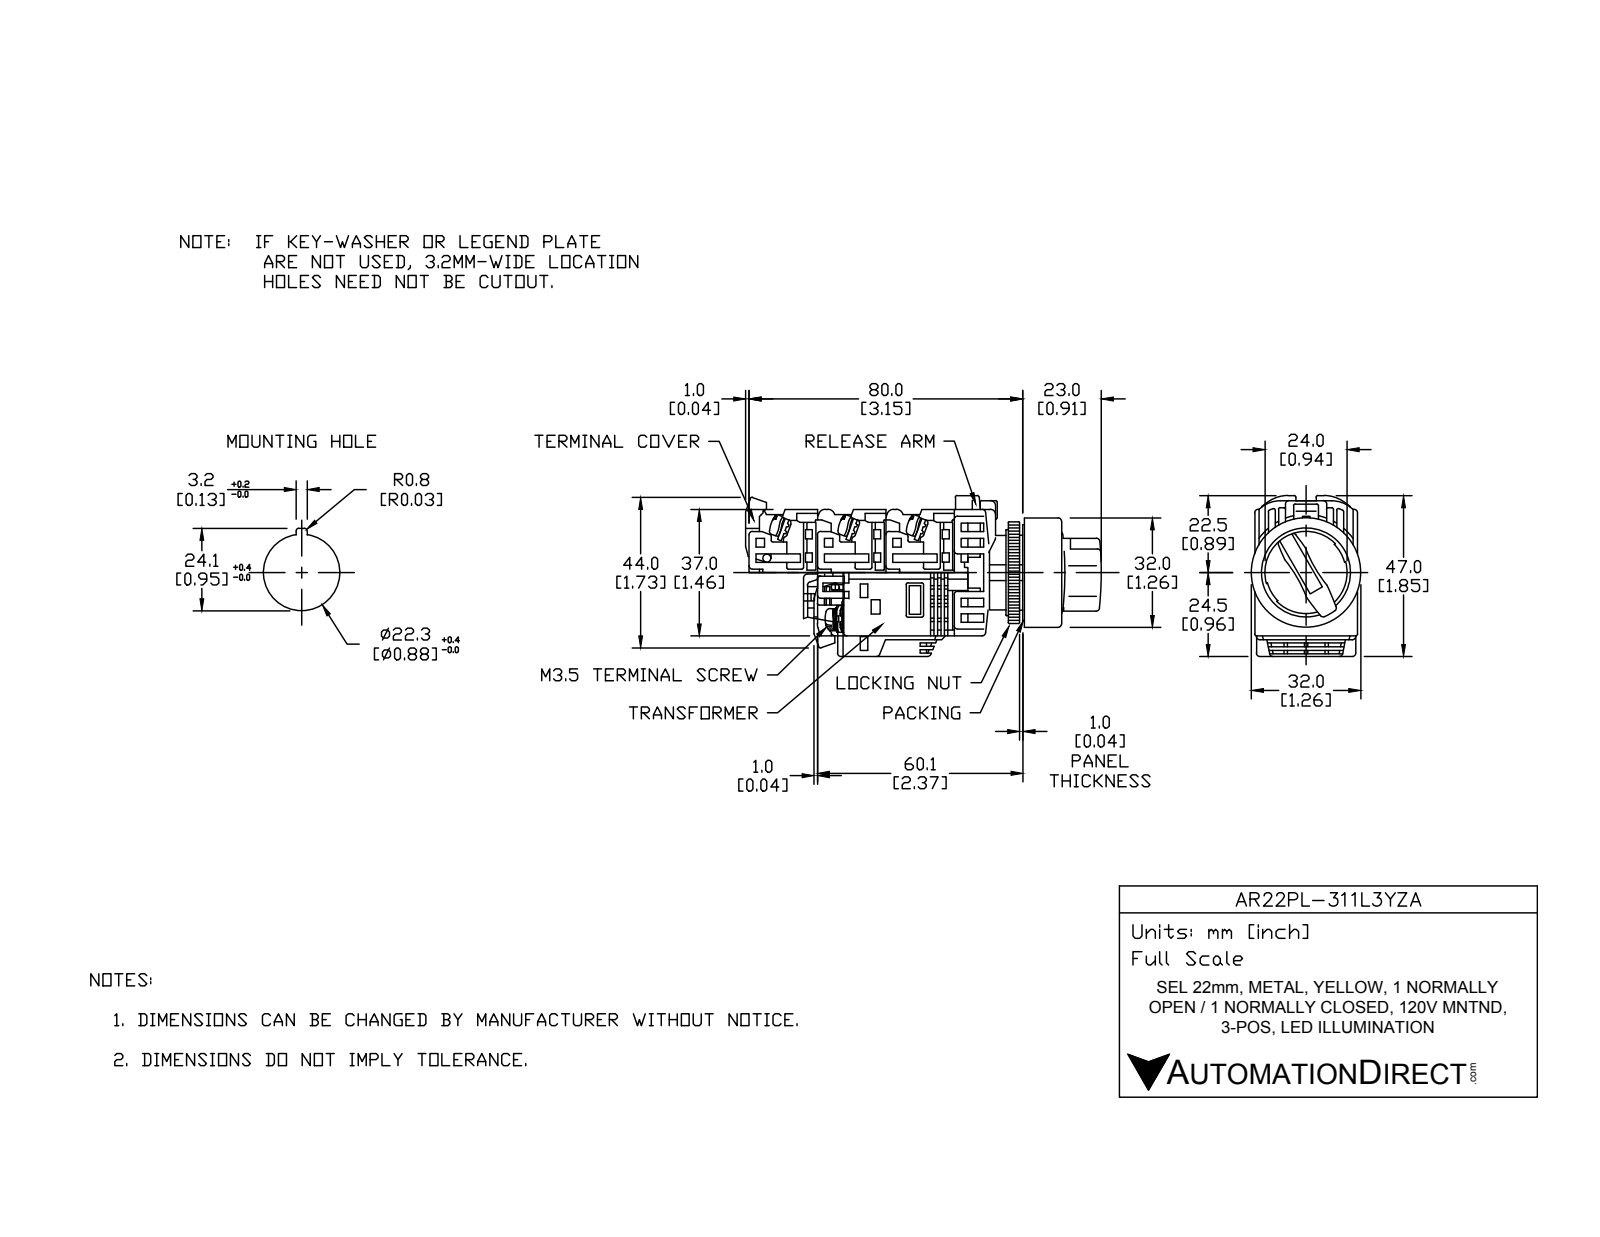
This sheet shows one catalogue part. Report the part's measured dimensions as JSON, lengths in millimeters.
{"part_name": "AR22PL-311L3YZA", "step_written_by": "SolidWorks 2017 (AUTOMOTIVE_DESIGN)", "units": "millimeters", "bodies": {"solids": 24, "faces": 602, "planar": 413, "cylindrical": 155, "other": 34}, "overall_size": [84.5, 43.81, 32], "volume_mm3": 58015, "surface_area_mm2": 31382, "round_holes": [[21.8, 1], [22, 1], [25, 1], [31, 1]], "round_bosses_or_shafts": [[5, 6], [32, 1], [30.5, 1], [29.8, 1], [24, 1], [21.75, 1], [17, 1]], "partial_cylinders_radius": [[0.5, 55], [1.75, 12], [1, 6], [5, 4], [4, 2], [12, 1], [16.59, 1], [17.59, 1]], "face_to_face_distances": [1, 20, 18, 29, 3, 40, 28.5, 0.5, 68.5, 21]}
